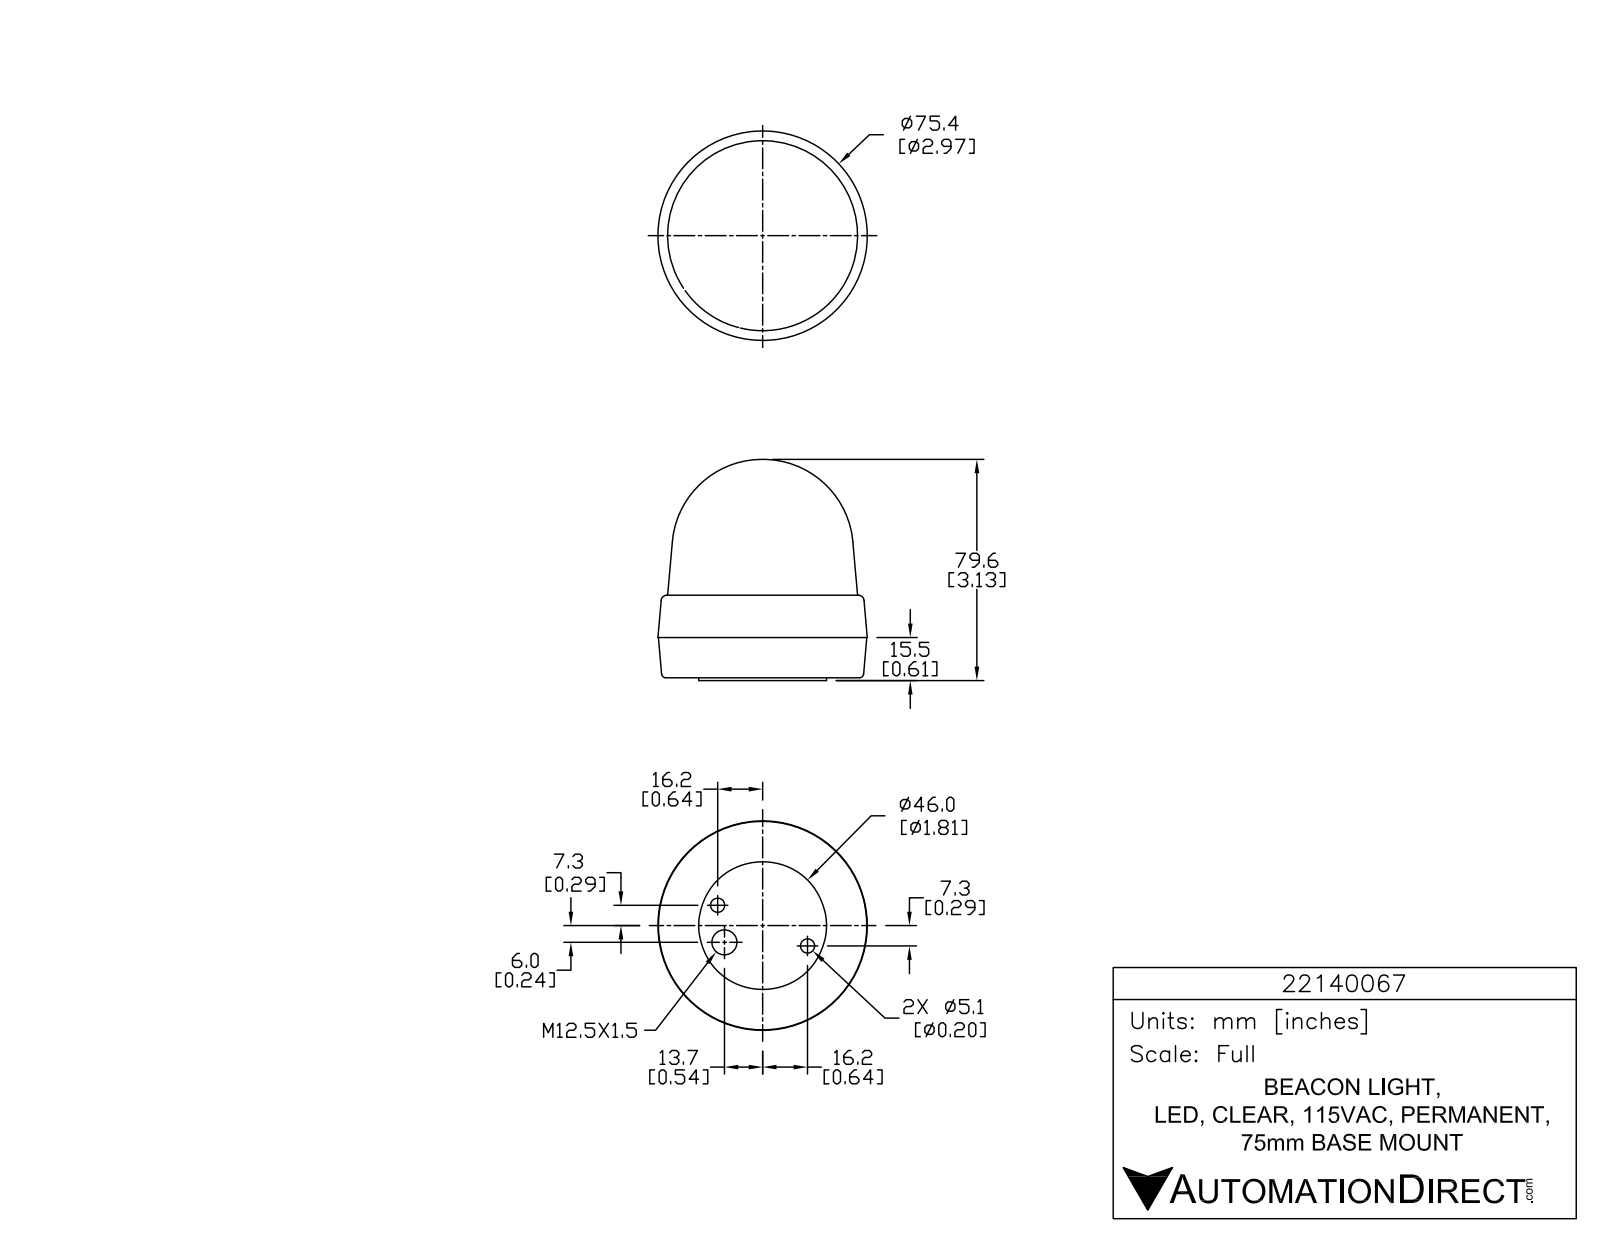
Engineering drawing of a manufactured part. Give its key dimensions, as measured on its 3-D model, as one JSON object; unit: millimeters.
{"part_name": "22140067", "step_written_by": "SolidWorks 2015 (AUTOMOTIVE_DESIGN)", "units": "millimeters", "bodies": {"solids": 1, "faces": 773, "planar": 526, "cylindrical": 163, "other": 84}, "overall_size": [79.6, 75.4, 75.4], "volume_mm3": 258800, "surface_area_mm2": 21740, "round_holes": [[1.5, 3], [5.1, 2], [9, 1]], "round_bosses_or_shafts": [[8.6, 3], [2.1, 3], [46, 1]], "partial_cylinders_radius": [[0.1, 9], [0.1, 6], [0.3, 6], [0.3, 6], [0.3, 6], [5, 6], [0.1, 3], [0.1, 3]], "face_to_face_distances": [1, 30.7, 29.7, 15.5, 14.5, 15.2, 39.8, 38.8, 24.3, 9.1], "hole_center_spacings": [13.6, 29.9, 35.5]}
